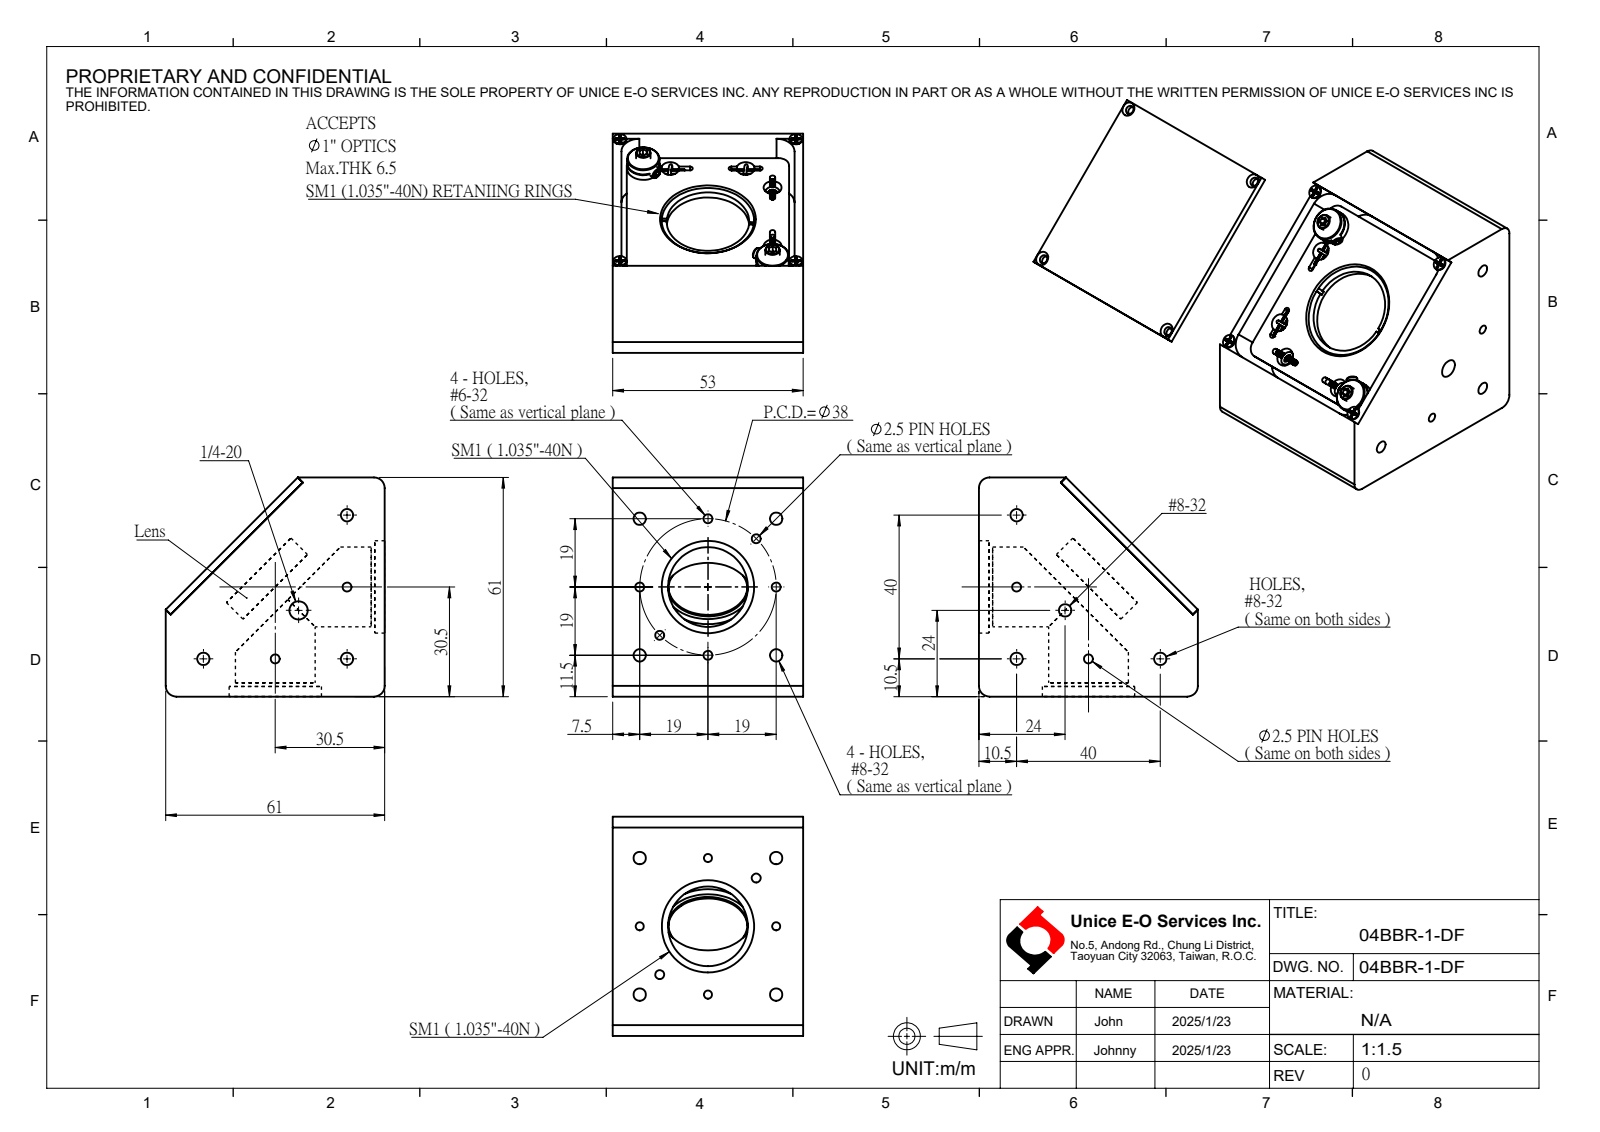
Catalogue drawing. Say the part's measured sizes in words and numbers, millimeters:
The part is named "04BBR-1-DF". Its 3-D file was written by "SolidWorks 2016 (CONFIG_CONTROL_DESIGN)". It is 9 solids with 459 faces: 146 planar, 185 cylindrical and 128 other. Overall it measures 61 by 61 by 53 millimeters. Its volume is 112 023 cubic millimeters and its surface area 41 369 square millimeters. Round holes: 18 of diameter 2.5, 12 of diameter 3.45, 5 of diameter 5, 4 of diameter 1.6, 4 of diameter 2.4, 3 of diameter 25.7, 2 of diameter 6, 2 of diameter 22.2, 2 of diameter 27.1, 1 of diameter 5.11, 1 of diameter 22, 1 of diameter 24.1. Round bosses or shafts: 4 of diameter 3.6, 4 of diameter 1.95, 1 of diameter 25.5, 1 of diameter 25.4. Partial cylindrical surfaces (rounded edges, fillets, slot ends): 12 of radius 0.75, 8 of radius 4, 7 of radius 3, 4 of radius 5, 1 of radius 1.5. The main face-to-face distances are 2.4, 53, 2, 61, 50.6, 17.7, 22.1, 20.1, 14.4, 5.7. The hole center spacings are 19, 26.87, 42.49, 38, 35.11, 14.54, 32.91, 7.86.
